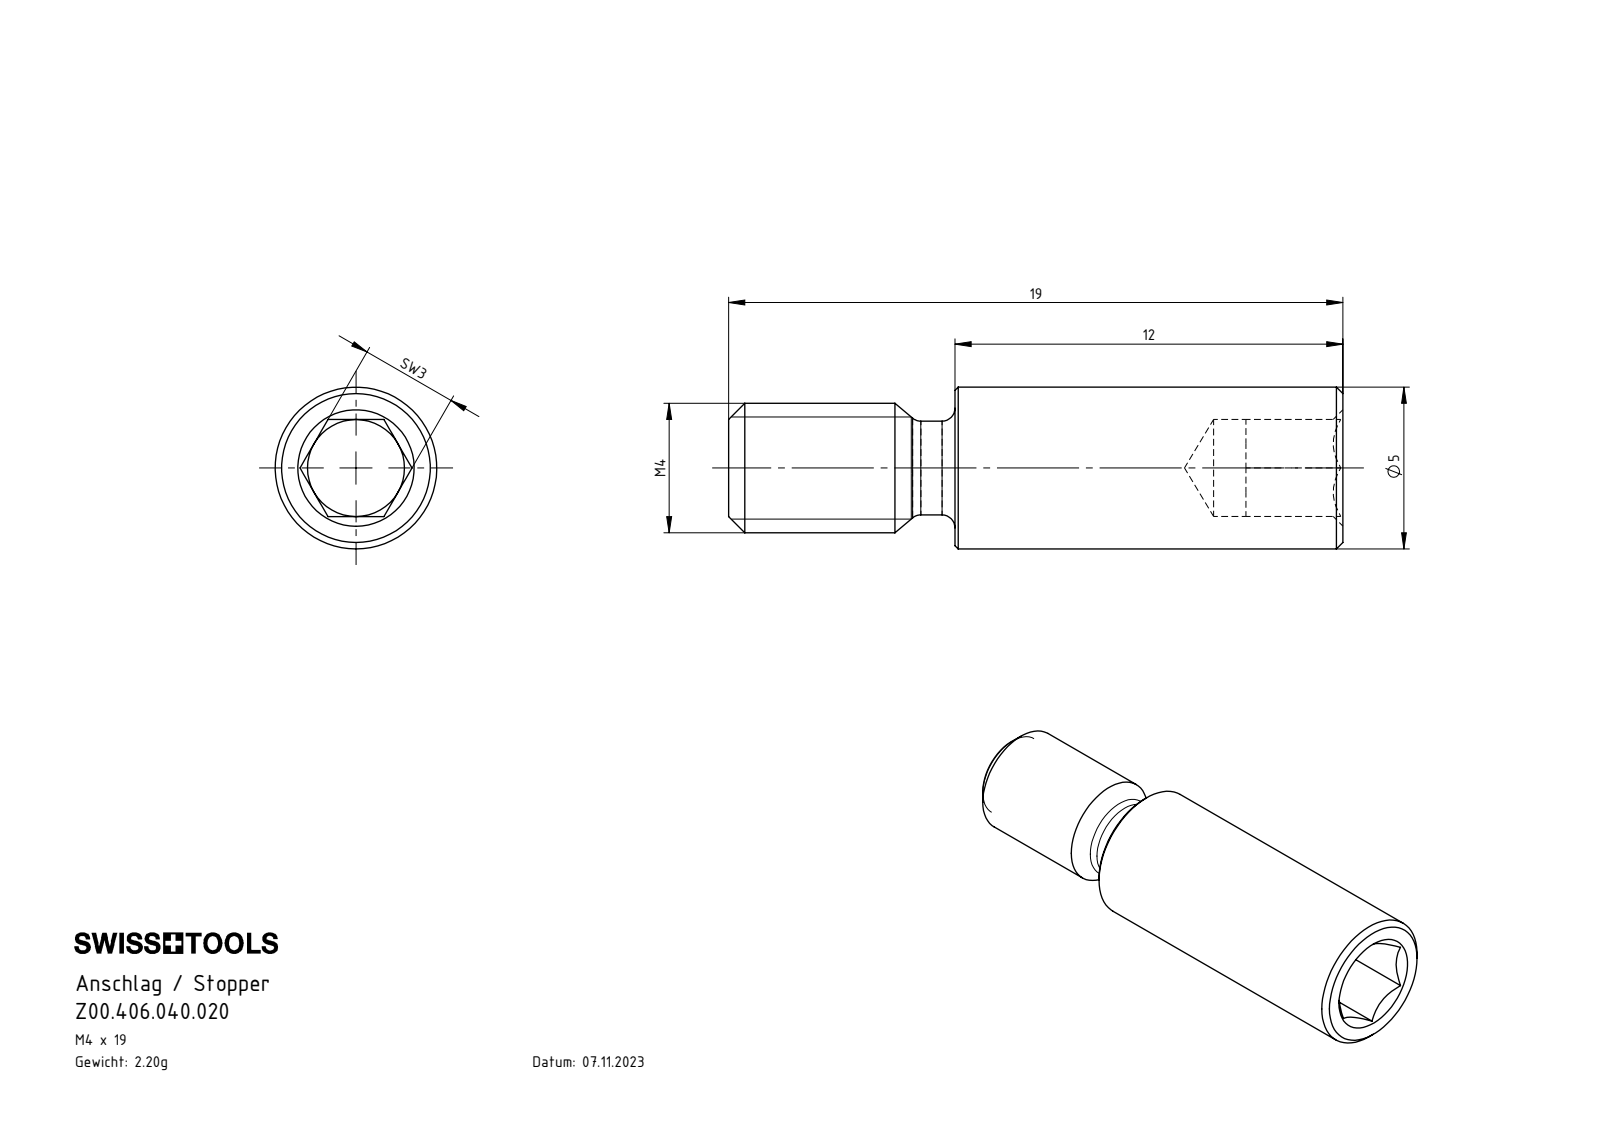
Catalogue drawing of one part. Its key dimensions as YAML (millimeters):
part_name: "Z00.406.040.020"
step_written_by: "SolidWorks 2022 (AUTOMOTIVE_DESIGN)"
units: millimeters
bodies: {solids: 1, faces: 39, planar: 15, cylindrical: 8, other: 16}
overall_size: [19, 5, 5]
volume: 280
surface_area: 351
round_holes:
  - {diameter: 3, count: 1}
round_bosses_or_shafts:
  - {diameter: 5, count: 1}
  - {diameter: 4, count: 1}
  - {diameter: 2.9, count: 1}
face_to_face_distances: [3, 7, 19, 12, 16, 9]
